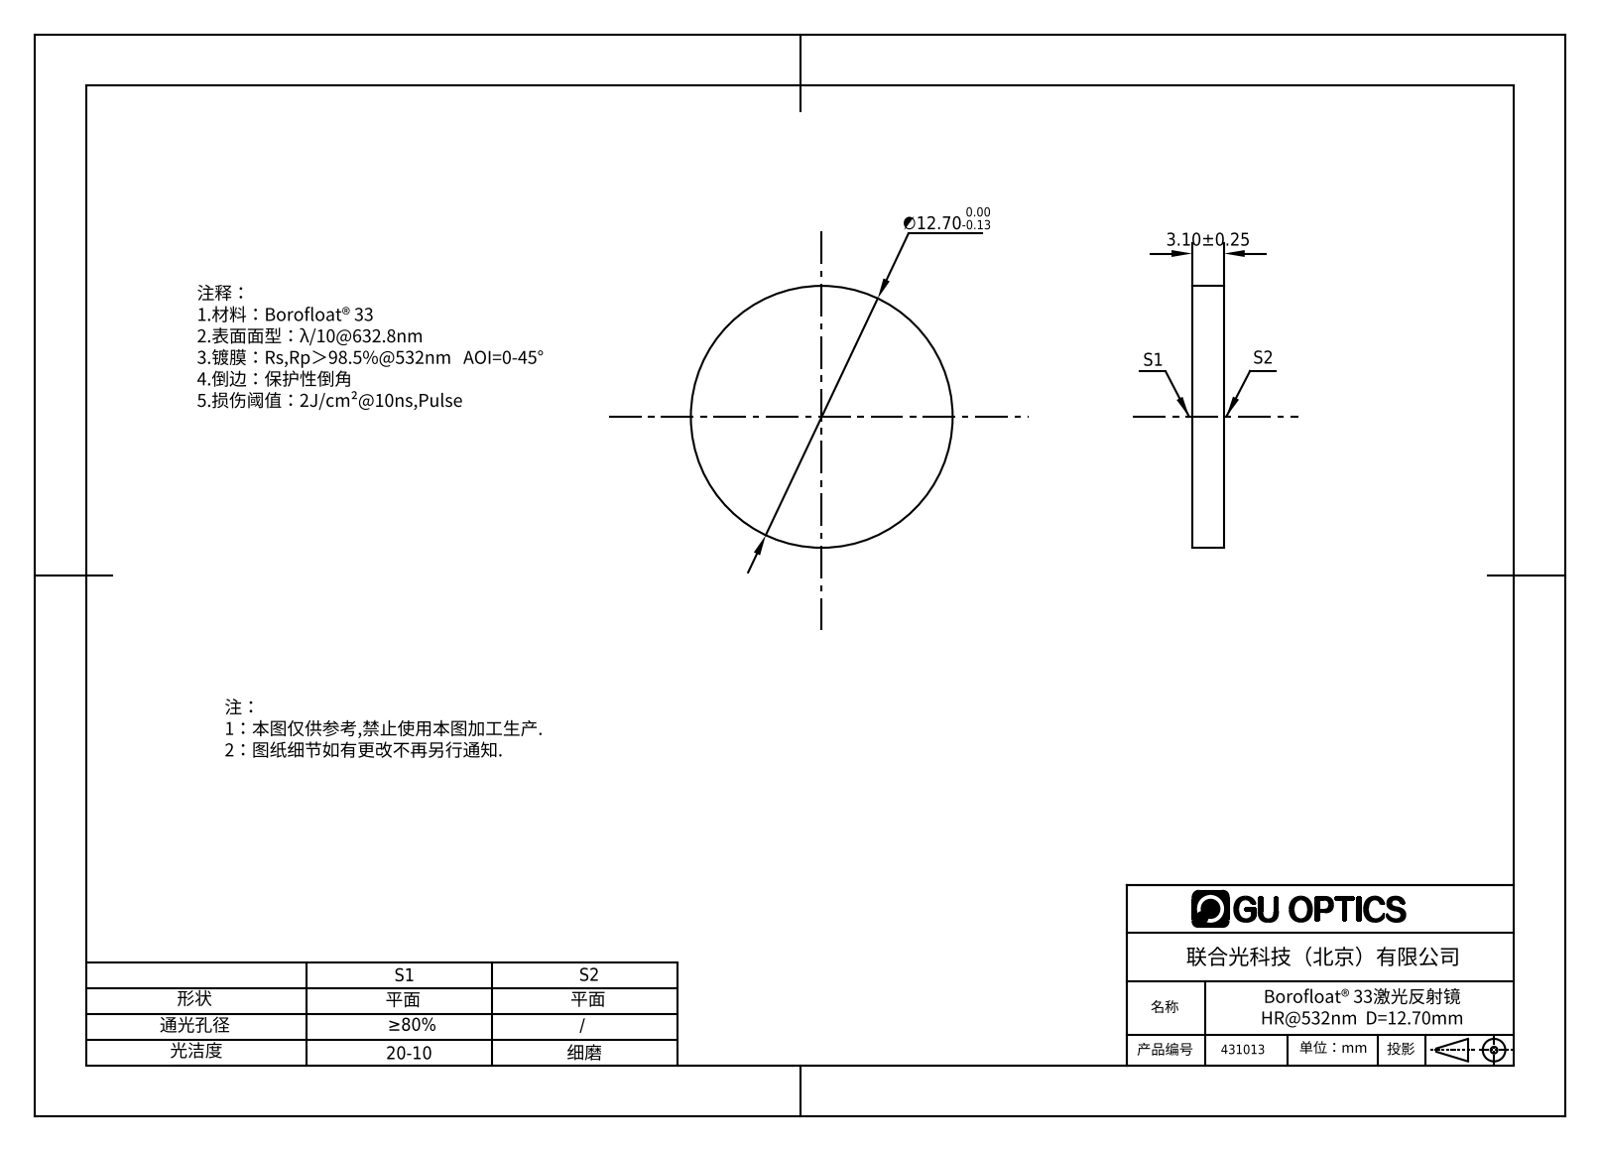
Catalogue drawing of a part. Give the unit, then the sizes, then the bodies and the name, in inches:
Units: inches
Overall size (bounding box): 0.5 × 0.5 × 0.122
Round bosses / shafts (diameter × count): ⌀0.5 ×1
Main face-to-face distances: 0.122
Volume: 0.024 in³ · Surface area: 0.584 in²
Bodies: 1 solid, 4 faces (2 planar, 2 cylindrical, 0 other)
Part name (STEP PRODUCT): 431008
STEP written by: SolidWorks 2016 (AUTOMOTIVE_DESIGN)
